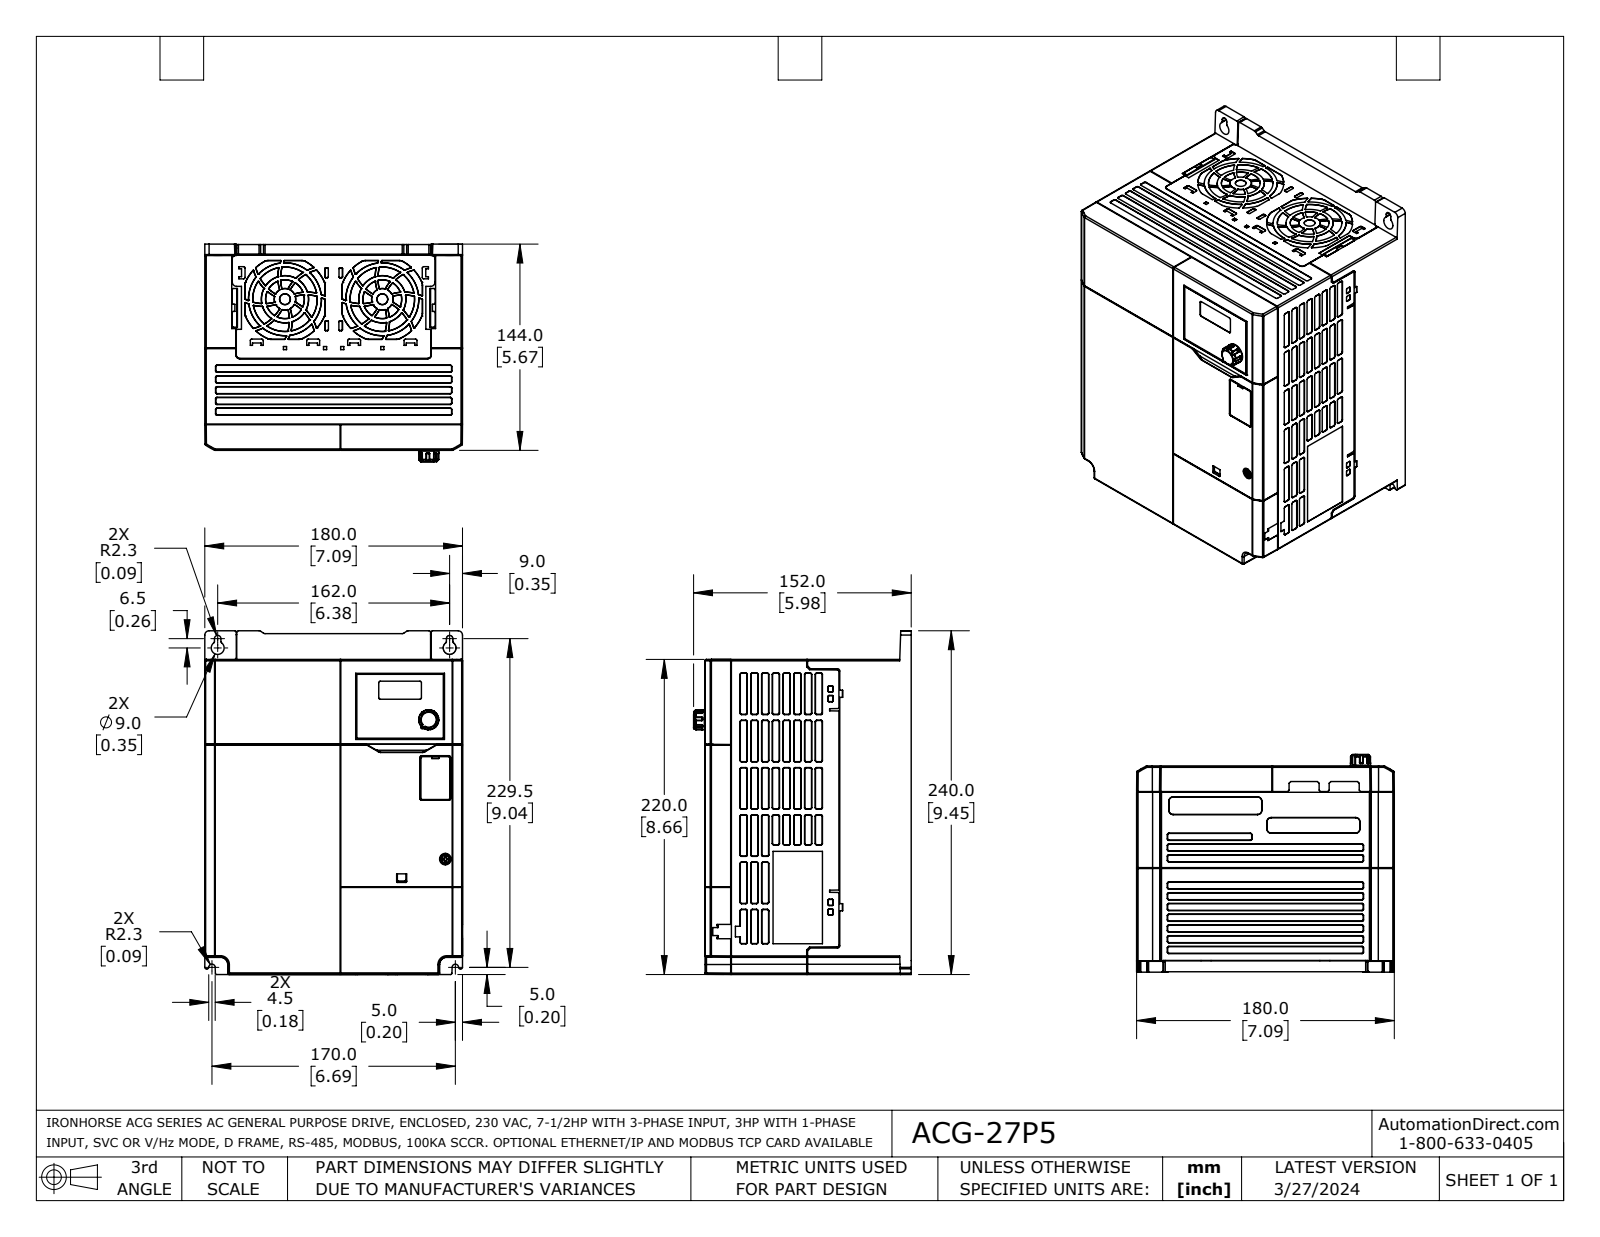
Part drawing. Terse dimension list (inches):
name: ACG-27P5
written by: SolidWorks 2021 (AUTOMOTIVE_DESIGN)
unit: in
bodies: 3 solids, 5218 faces (2417 planar, 929 cylindrical, 1872 other)
size: 9.449 × 7.087 × 5.984
volume: 87.68 in³; area: 753.3 in²
holes: 1× ⌀0.039, 1× ⌀0.276, 1× ⌀0.417, 1× ⌀0.472
bosses: 1× ⌀0.551, 1× ⌀0.543, 1× ⌀0.236
rounds: 587× R0.02, 88× R0.039, 65× R0.008, 27× R0.012, 16× R0.024, 10× R0.047, 5× R0.079, 4× R0.059
face distances: 5.316, 0.165, 5.48, 0.134, 5.346, 0.031, 0.039, 7.047, 0.126, 5.354
hole spacings: 0.276, 2.155, 2.191, 3.675, 3.858, 5.693
